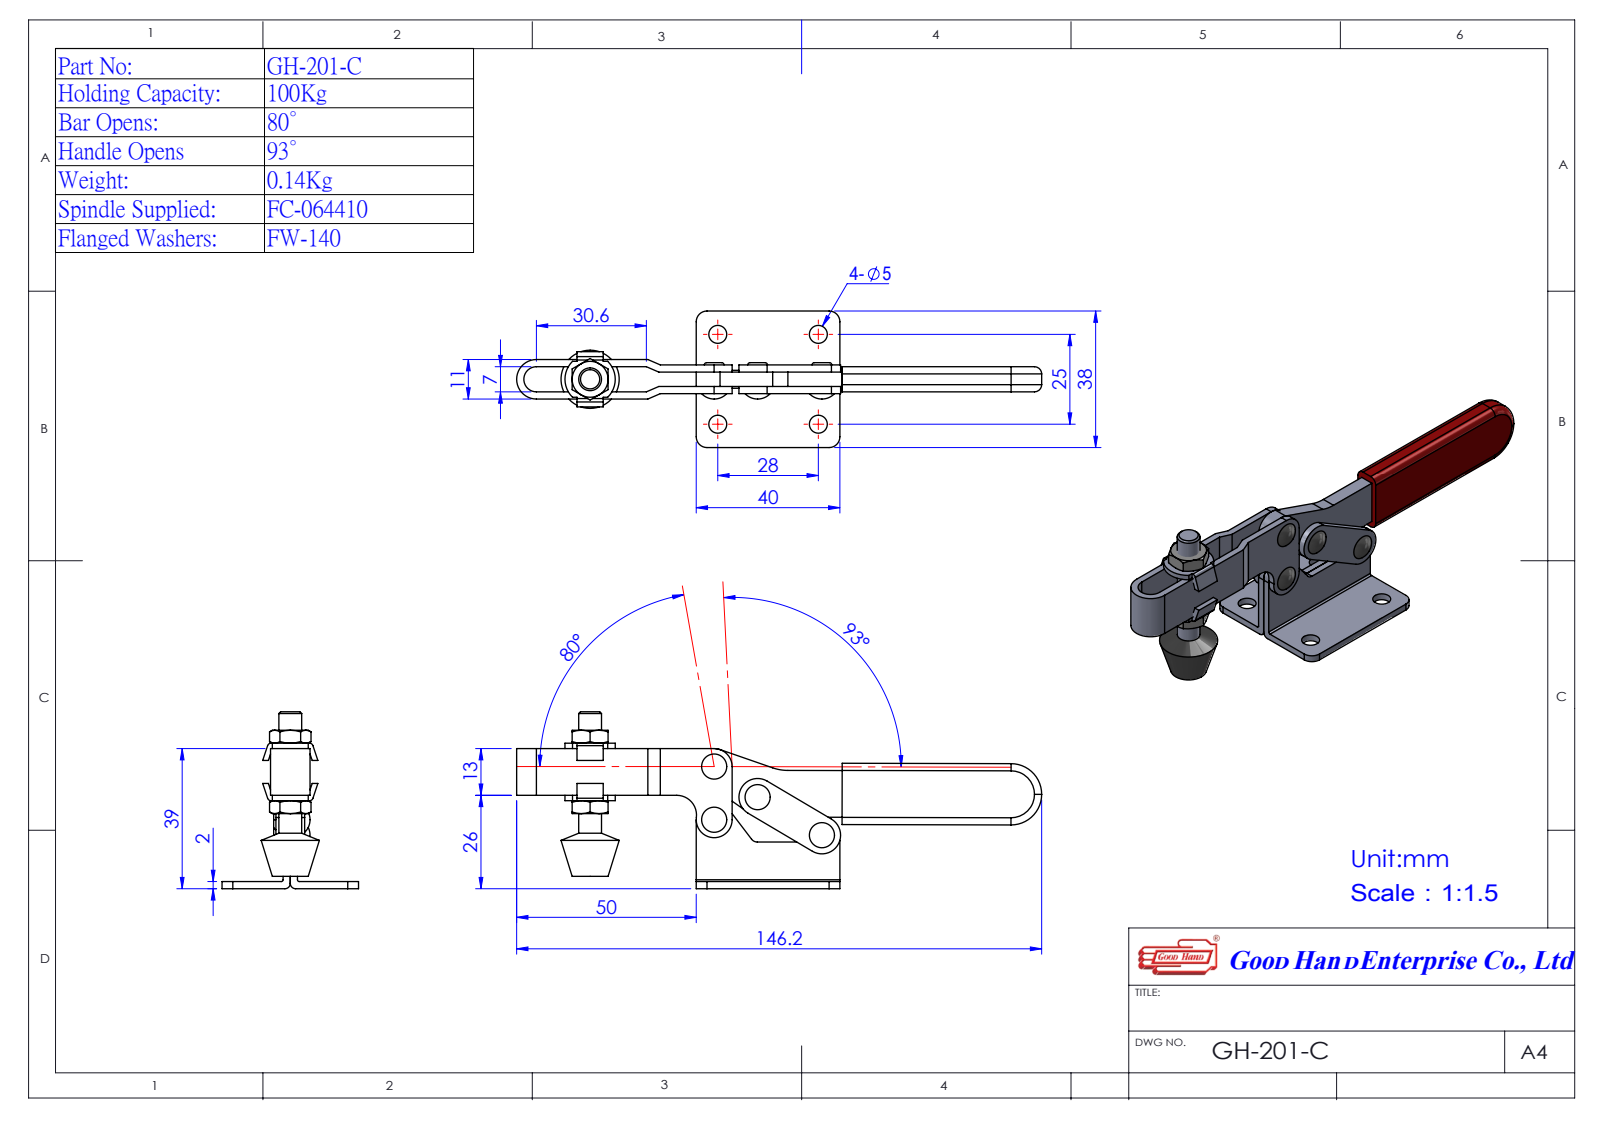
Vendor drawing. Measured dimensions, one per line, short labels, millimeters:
name: Group2^GH-201-C(簡化); GH-201-C(簡化); Group5^GH-201-C(簡化); Group4^GH-201-C(簡化) (+2 more)
written by: SolidWorks 2016 (AUTOMOTIVE_DESIGN)
unit: mm
bodies: 5 solids, 227 faces (105 planar, 76 cylindrical, 46 other)
size: 146.19 × 49.25 × 38
volume: 22 395 mm³; area: 17 191 mm²
holes: 4× ⌀3.5, 4× ⌀5
bosses: 1× ⌀10, 1× ⌀6.35
rounds: 5× R1, 4× R3, 2× R5, 2× R5.2, 2× R5.5, 1× R2, 1× R3.5, 1× R5.03
face distances: 1.5, 2, 5.5, 7.5, 4, 7, 0.5, 6, 9, 3.5
hole spacings: 25, 28, 37.54, 13.62, 14.79, 14.8, 20.8, 30.31
